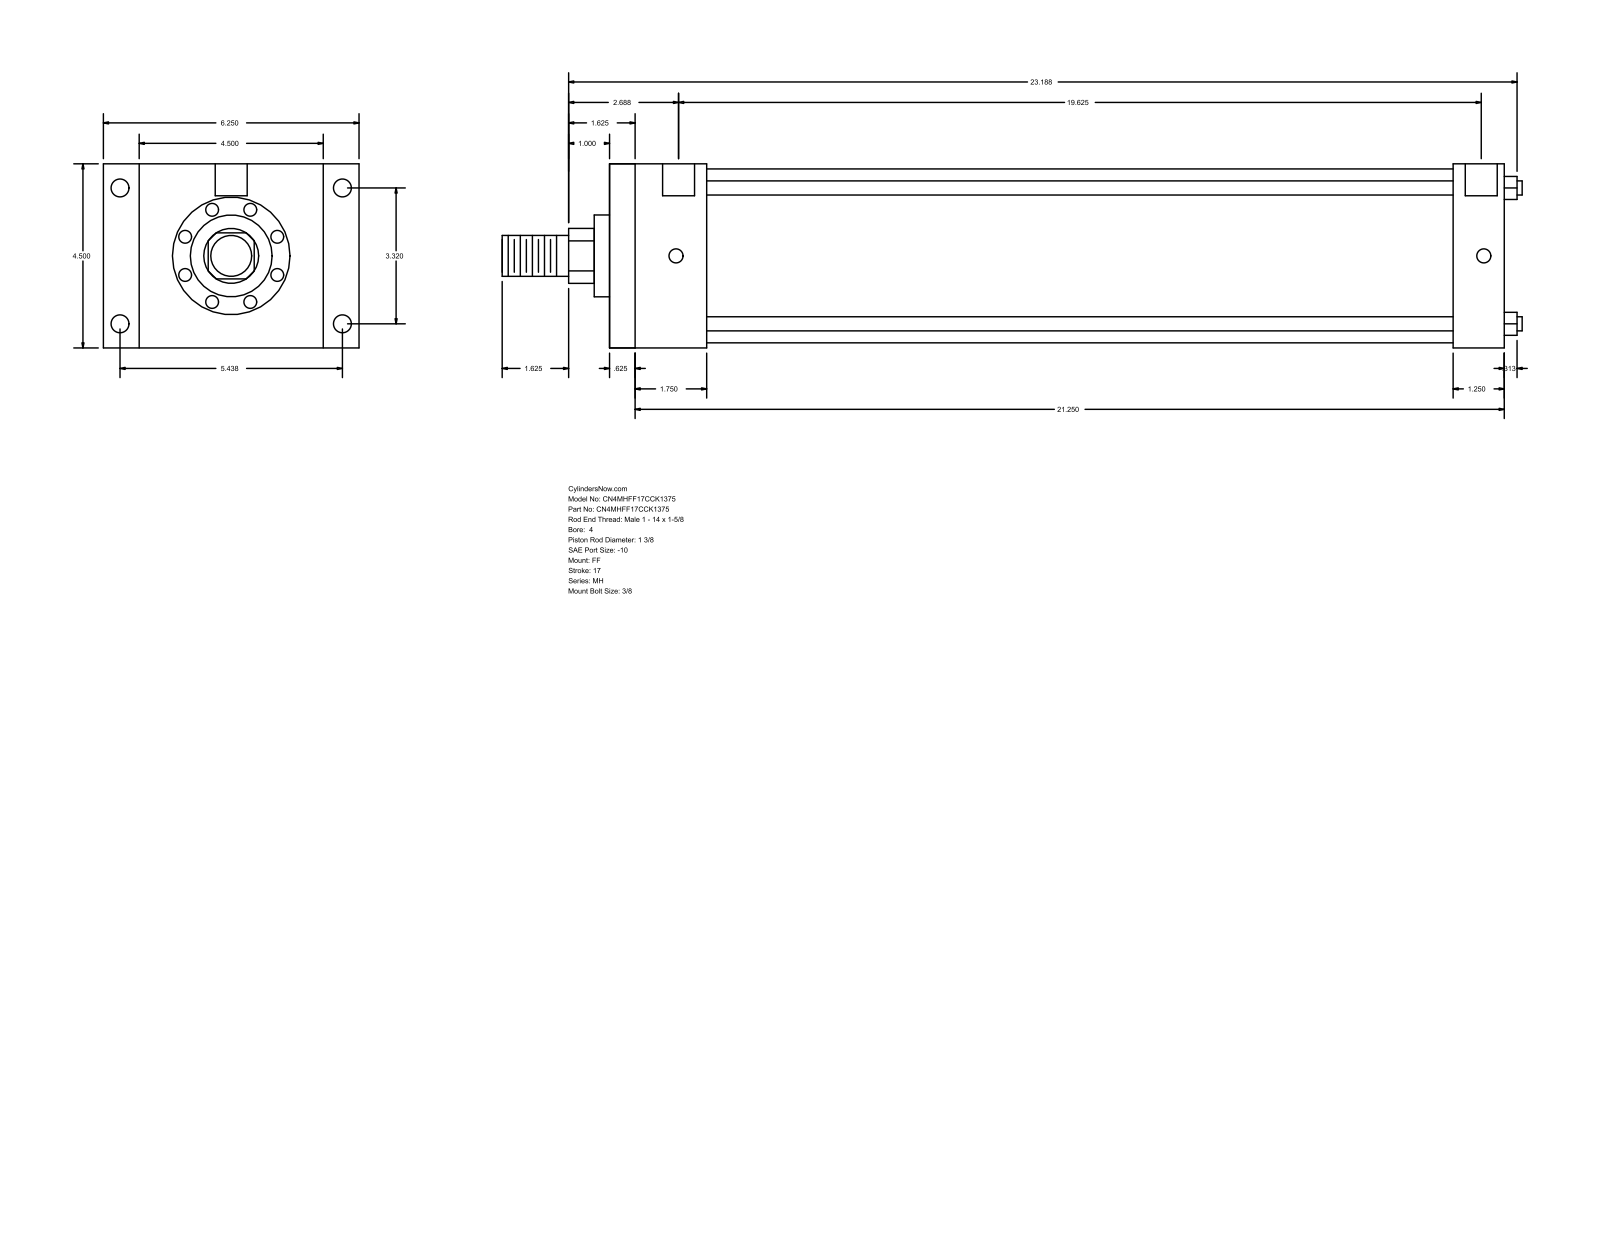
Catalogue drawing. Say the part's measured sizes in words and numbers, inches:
The part is named "MH_FF__0400_1.375". Its 3-D file was written by "GSSL Pune (CONFIG_CONTROL_DESIGN)". It is 0 solids with 92 faces: 64 planar, 28 cylindrical and 0 other. Overall it measures 24.937 by 6.25 by 4.5 inches. Round holes: 4 of diameter 0.344, 4 of diameter 0.438, 2 of diameter 0.781. Round bosses or shafts: 4 of diameter 0.345, 1 of diameter 4.25, 1 of diameter 2, 1 of diameter 1.375, 1 of diameter 1. Partial cylindrical surfaces (rounded edges, fillets, slot ends): 1 of radius 0.672. The main face-to-face distances are 4.5, 21.875, 0.625, 21.25, 2.375, 1.75, 19.5, 20.625, 20, 18.25. The hole center spacings are 0.063, 3.32, 5.438, 6.371, 19.688, 19.75, 19.625.
